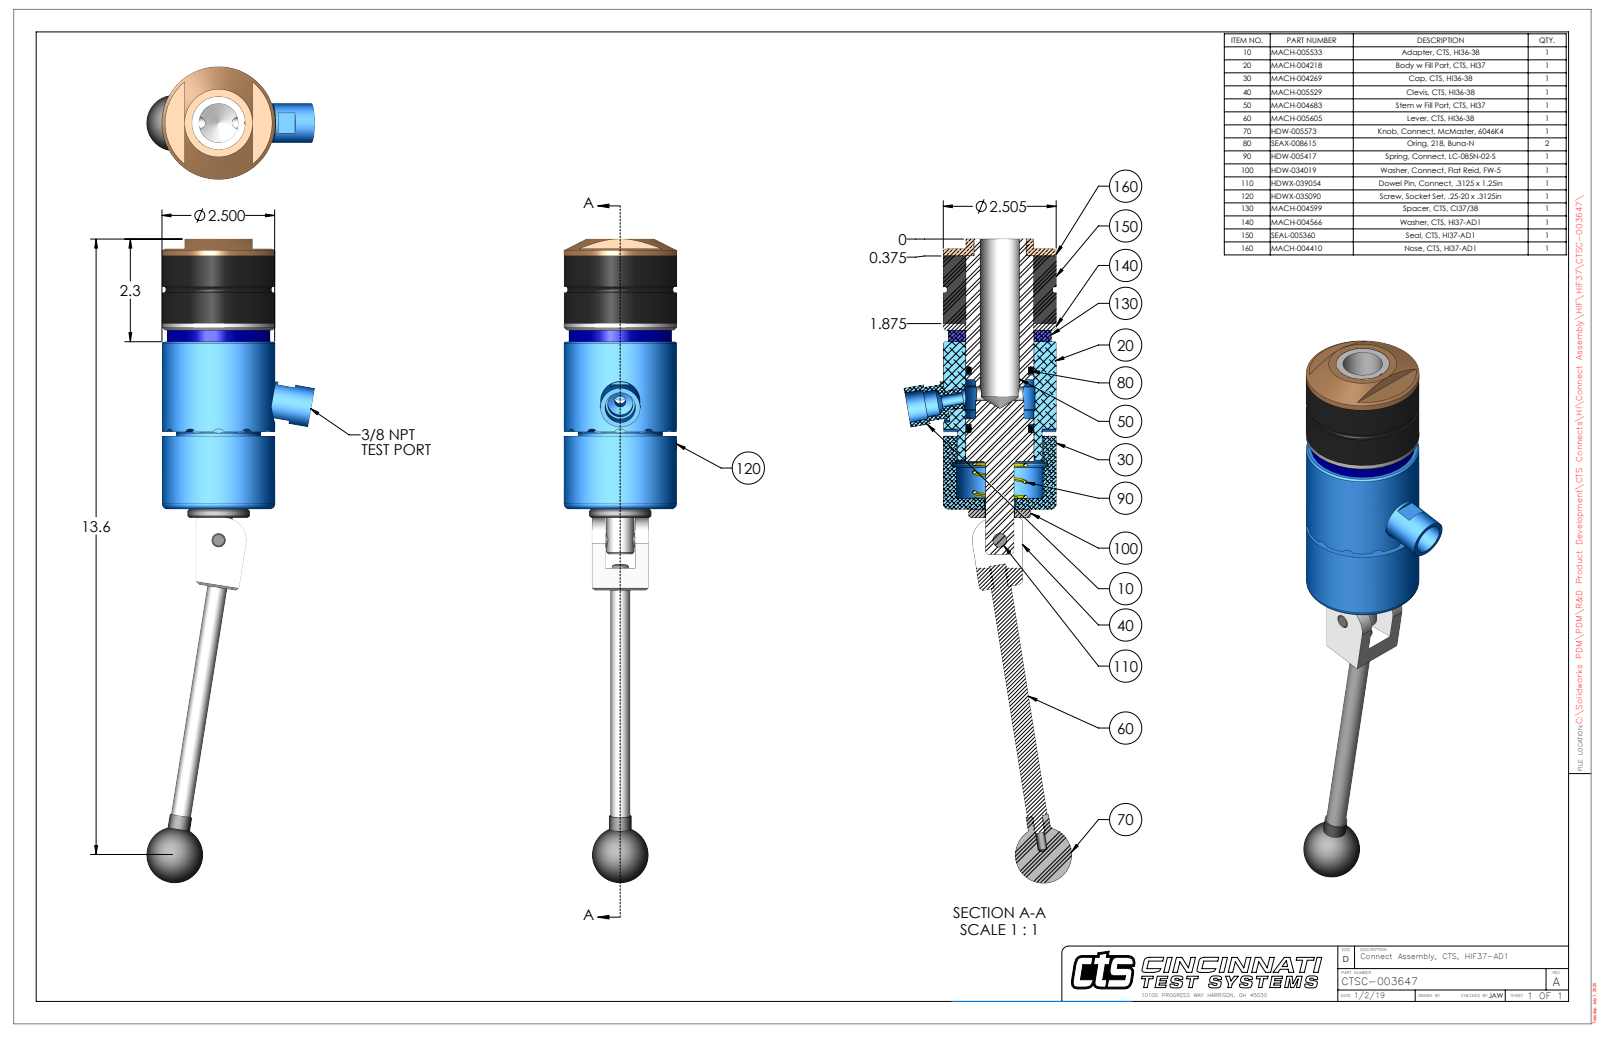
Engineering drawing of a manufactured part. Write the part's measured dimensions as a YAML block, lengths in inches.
part_name: "CTSC-003647"
step_written_by: "SolidWorks 2023 (AUTOMOTIVE_DESIGN)"
units: inches
bodies: {solids: 11, faces: 313, planar: 110, cylindrical: 129, other: 74}
overall_size: [14.275, 3.716, 2.505]
volume: 30.14
surface_area: 154.5
round_holes:
  - {diameter: 0.201, count: 2}
  - {diameter: 0.15, count: 1}
  - {diameter: 0.25, count: 1}
  - {diameter: 0.311, count: 1}
  - {diameter: 0.312, count: 1}
  - {diameter: 0.313, count: 1}
  - {diameter: 0.314, count: 1}
  - {diameter: 0.562, count: 1}
  - {diameter: 0.656, count: 1}
  - {diameter: 0.696, count: 1}
  - {diameter: 0.875, count: 1}
  - {diameter: 1.172, count: 1}
round_bosses_or_shafts:
  - {diameter: 2.505, count: 1}
  - {diameter: 2.505, count: 1}
  - {diameter: 2.5, count: 1}
  - {diameter: 2.281, count: 1}
  - {diameter: 1.875, count: 1}
  - {diameter: 1.5, count: 1}
  - {diameter: 1.496, count: 1}
  - {diameter: 1.38, count: 1}
partial_cylinders:
  - {radius: 0.12, count: 12}
  - {radius: 0.029, count: 2}
  - {radius: 0.19, count: 1}
  - {radius: 0.195, count: 1}
  - {radius: 0.47, count: 1}
  - {radius: 0.475, count: 1}
  - {radius: 0.5, count: 1}
  - {radius: 1.188, count: 1}
face_to_face_distances: [1.5, 0.25, 0.402, 1.902, 0.152, 1.652, 3.713, 3.963, 4.115, 5.615]
hole_center_spacings: [0.74, 2.118, 2.858]
